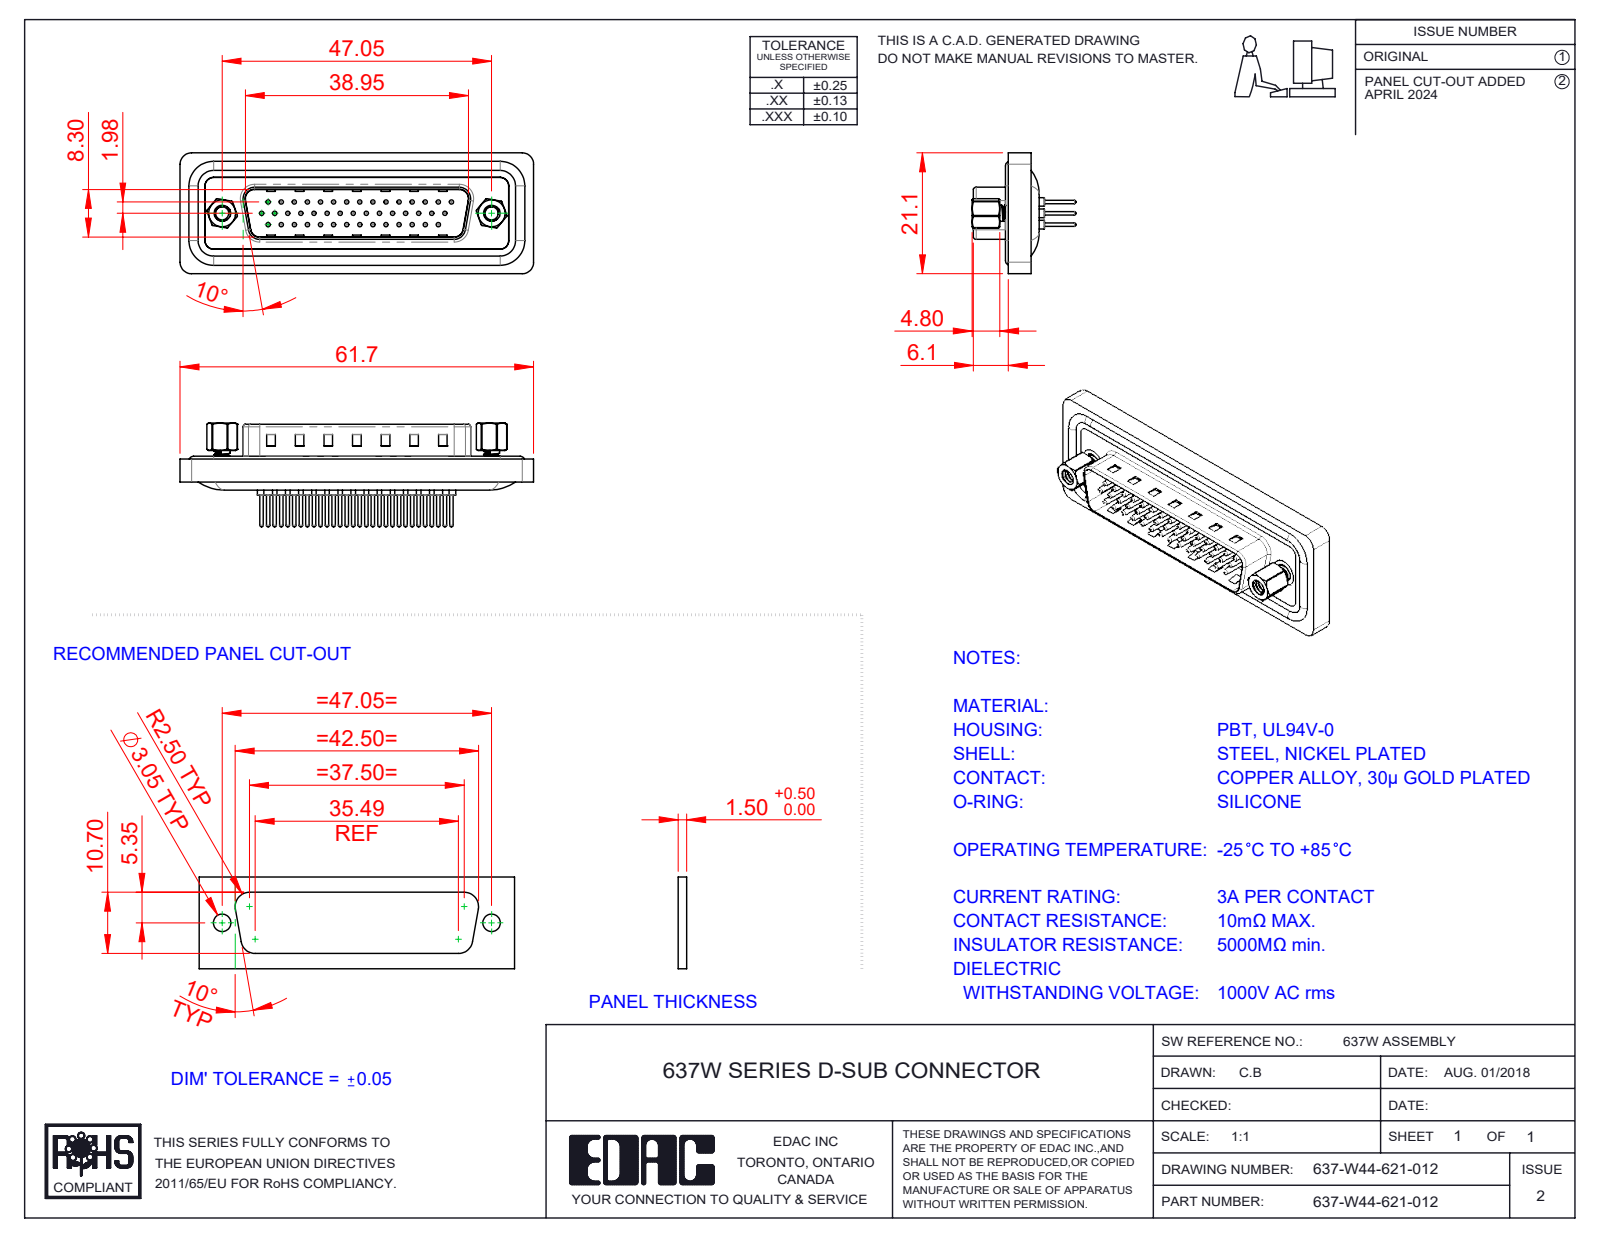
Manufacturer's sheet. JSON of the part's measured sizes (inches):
{"part_name": "637W Waterproof Housing_44 Contacts; 637W Contact Row 2_21; 637W Contact Row 3_21; 637W 4-40 Threaded Rivet (+5 more)", "step_written_by": "SolidWorks 2016 (CONFIG_CONTROL_DESIGN)", "units": "inches", "bodies": {"solids": 52, "faces": 2234, "planar": 513, "cylindrical": 920, "other": 801}, "overall_size": [2.431, 0.831, 0.705], "volume_in3": 0.389, "surface_area_in2": 18.64, "round_holes": [[0.03, 44], [0.059, 44], [0.063, 44], [0.079, 44], [0.089, 2], [0.09, 2], [0.157, 2], [0.189, 2], [0.197, 2]], "round_bosses_or_shafts": [[0.024, 44], [0.059, 21], [0.063, 4], [0.193, 2], [0.11, 2], [0.197, 1]], "partial_cylinders_radius": [[0.079, 14], [0.059, 13], [0.02, 8], [0.106, 6], [0.035, 4], [0.063, 4], [0.169, 4], [0.016, 2]], "face_to_face_distances": [0.016, 0.063, 0.098, 0.114, 0.043, 0.222, 0.608, 0.03, 0.252, 0.579], "hole_center_spacings": [0.09, 0.156, 0.09, 0.18, 0.324, 0.27, 0.45, 0.59]}
